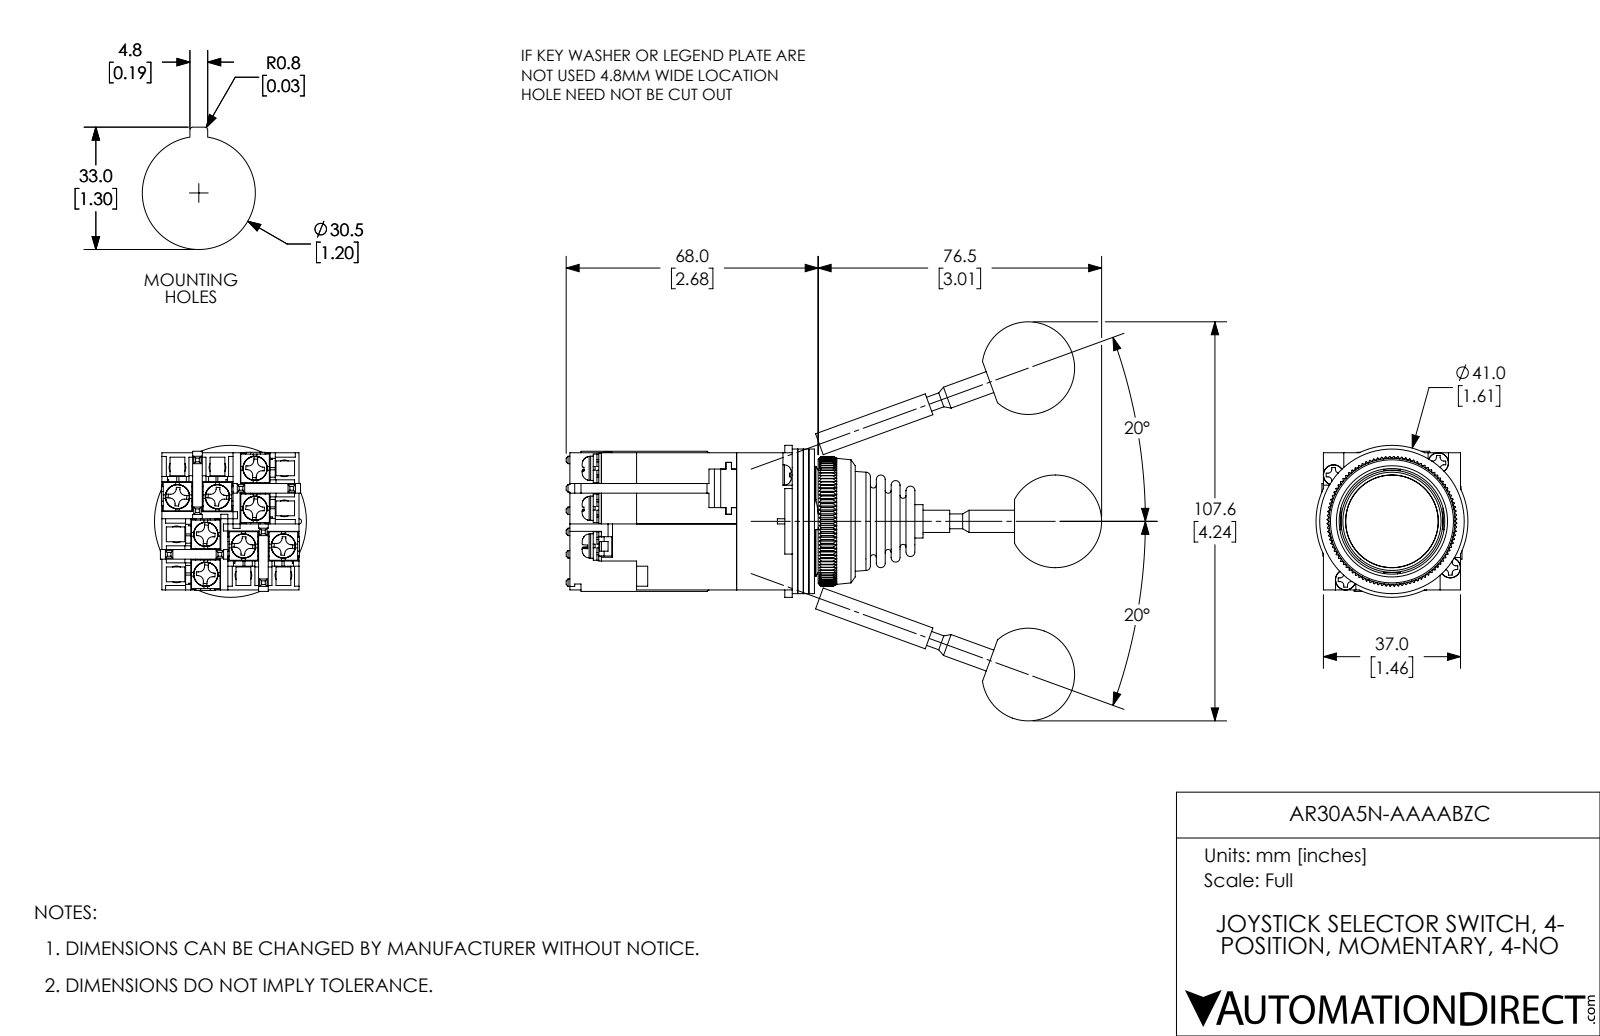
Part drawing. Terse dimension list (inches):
name: AR30A5N-AAAABZC
written by: SolidWorks 2017 (AUTOMOTIVE_DESIGN)
unit: in
bodies: 52 solids, 2889 faces (2186 planar, 417 cylindrical, 286 other)
size: 5.689 × 1.614 × 1.614
volume: 5.335 in³; area: 92.62 in²
holes: 12× ⌀0.118, 8× ⌀0.138, 8× ⌀0.142, 1× ⌀0.315, 1× ⌀0.874, 1× ⌀1.122, 1× ⌀1.173
bosses: 8× ⌀0.26, 1× ⌀1.535, 1× ⌀1.181, 1× ⌀0.984, 1× ⌀0.354, 1× ⌀0.236, 1× ⌀0.157
rounds: 32× R0.059, 16× R0.029, 16× R0.039, 16× R0.057, 16× R0.089, 4× R0.108, 1× R0.028, 1× R0.398
face distances: 0.701, 0.059, 0.756, 0.055, 1.457, 0.177, 0.118, 0.449, 0.114, 0.823
hole spacings: 0.296, 0.365, 0.756, 0.792, 0.875, 1.12, 0.419, 0.5
